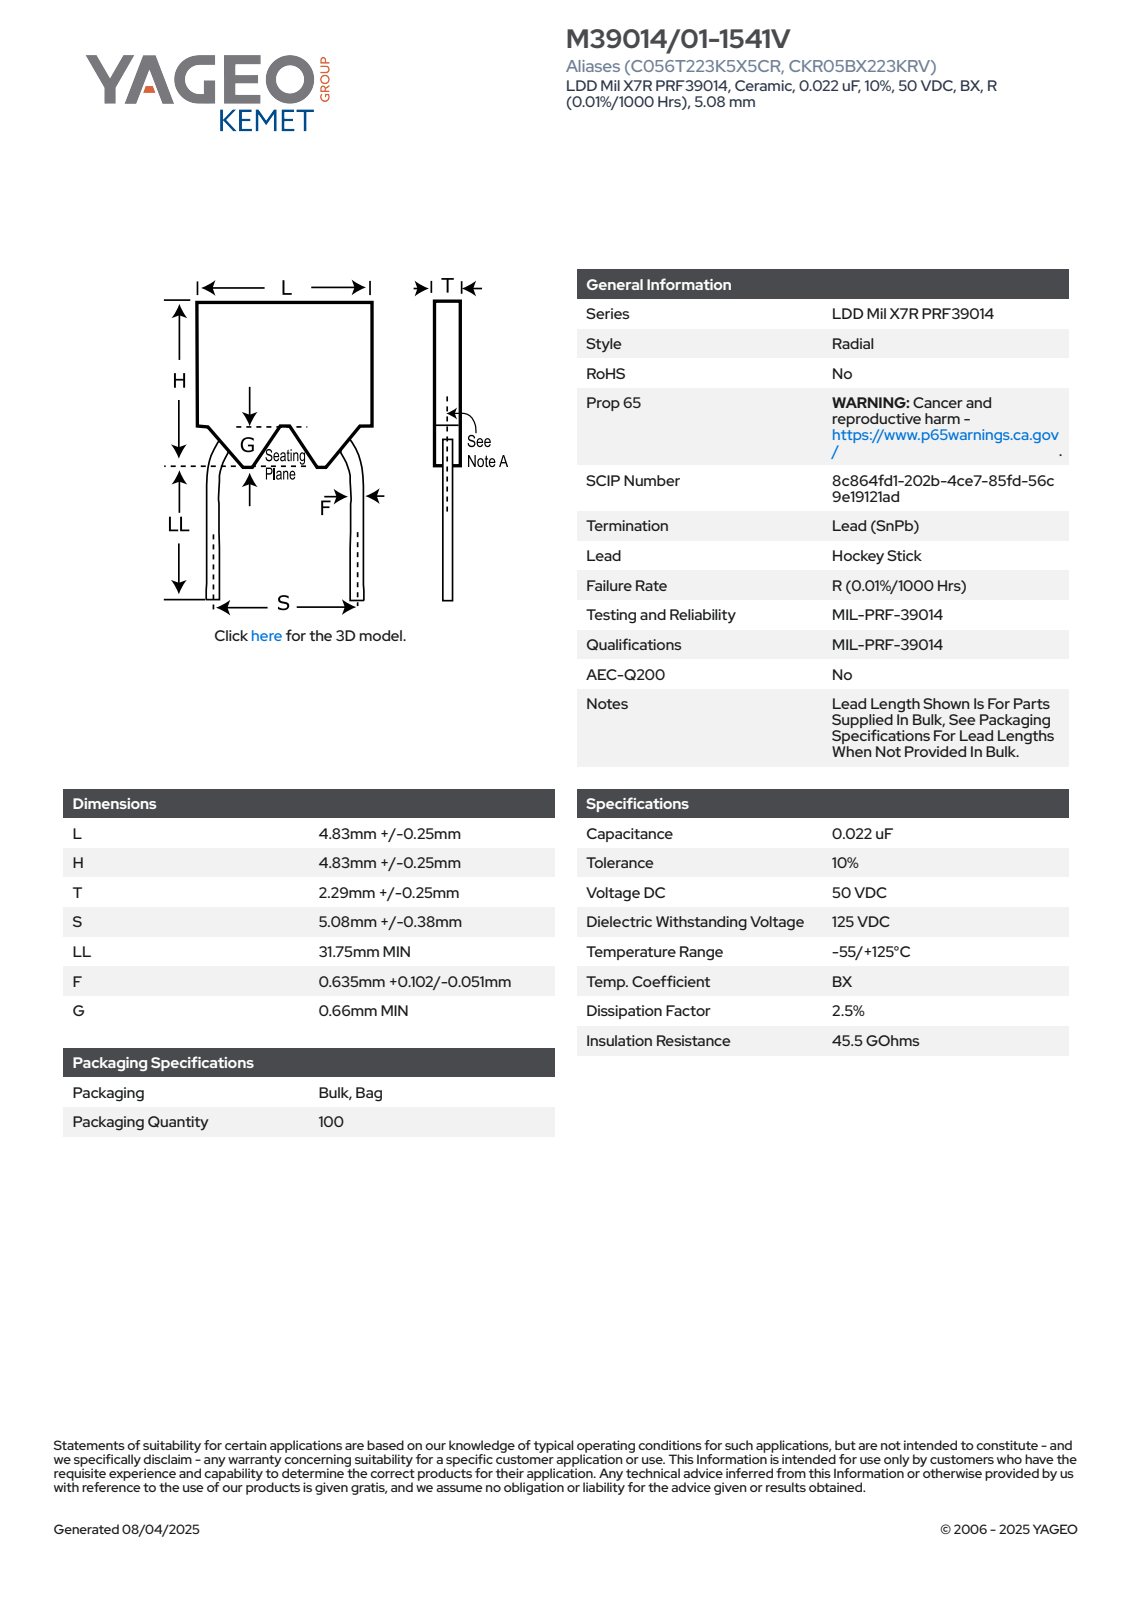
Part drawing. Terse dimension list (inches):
name: CCRM_VHS_C056_L5.08H5.08T2.54S5.08LL31.75F0.635G0.66
written by: SolidWorks 2014 (AUTOMOTIVE_DESIGN)
unit: in
bodies: 4 solids, 85 faces (73 planar, 0 cylindrical, 12 other)
size: 1.45 × 0.223 × 0.1
volume: 0.005 in³; area: 0.35 in²
face distances: 0.1, 0.2, 0.174, 0.058, 0.058, 0.026, 1.25, 1.276, 1.45, 0.03
